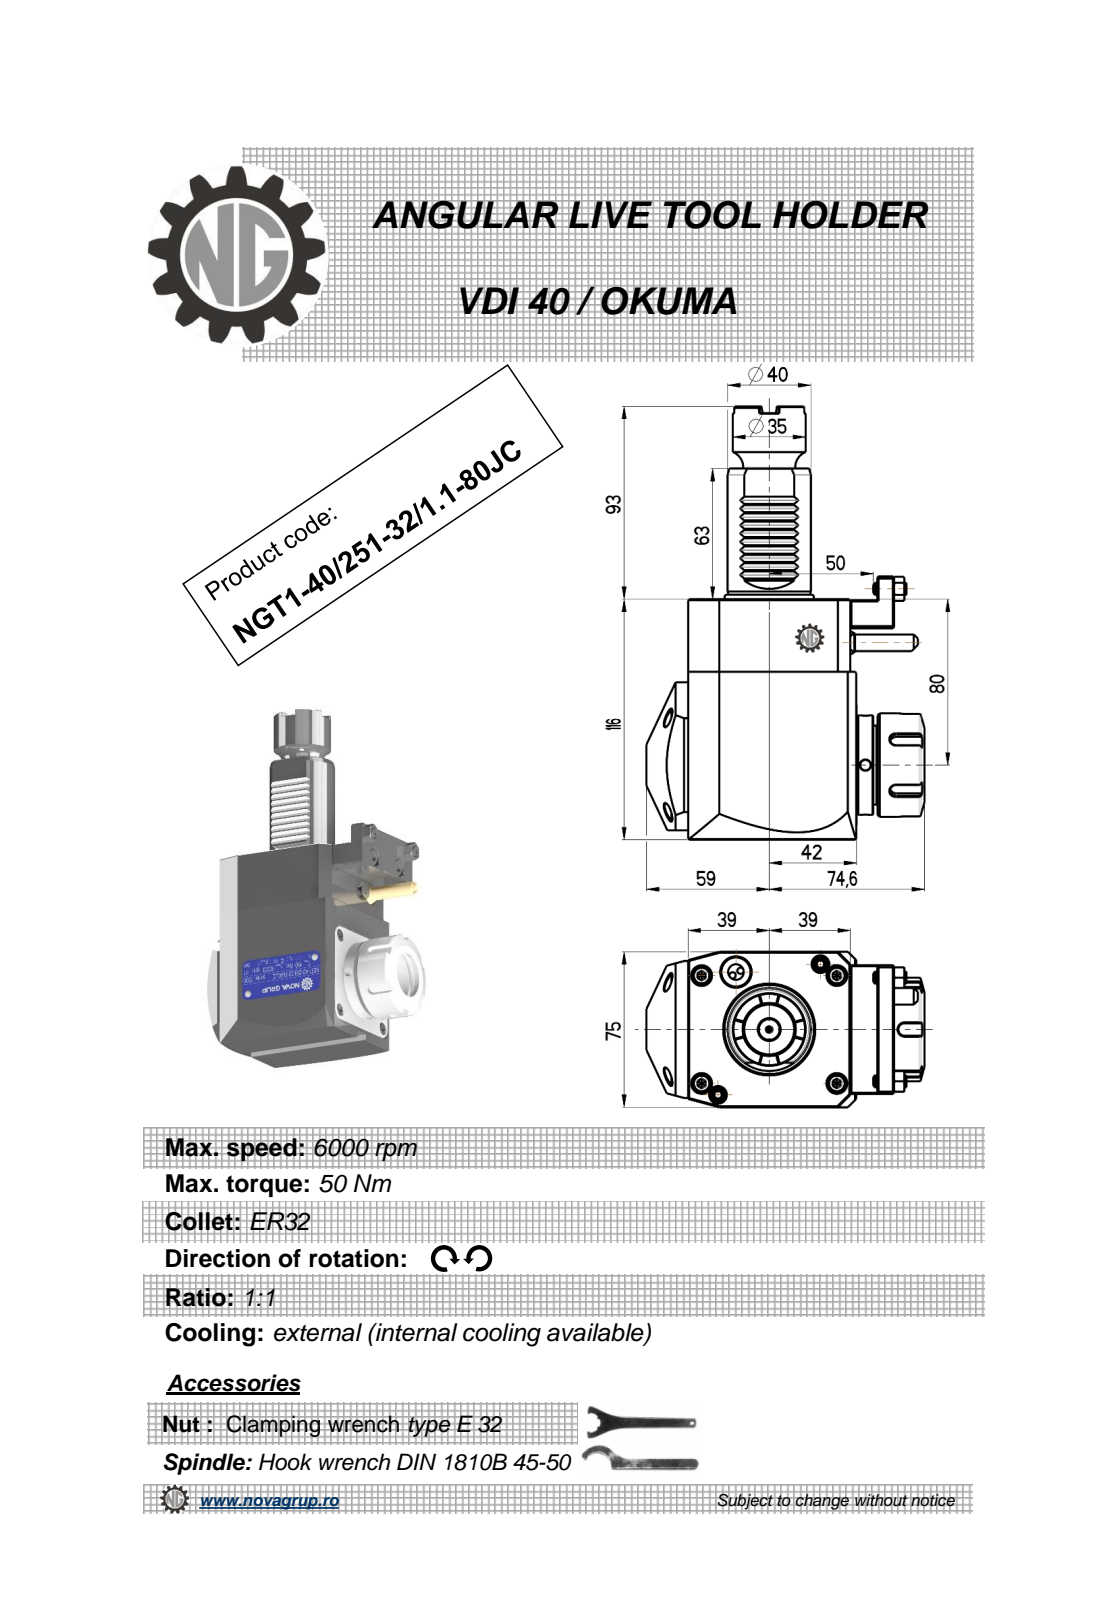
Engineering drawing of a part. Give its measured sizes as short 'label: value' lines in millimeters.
name: NGT1_40_251_32_1_1_80JC
written by: PRO/ENGINEER BY PARAMETRIC TECHNOLOGY CORPORATION, 2010280 (CONFIG_CONTROL_DESIGN)
unit: mm
bodies: 1 solid, 460 faces (195 planar, 86 cylindrical, 179 other)
size: 209 × 133.6 × 76.6
volume: 917 200 mm³; area: 75 631 mm²
holes: 3× ⌀5, 1× ⌀3, 1× ⌀25, 1× ⌀27
bosses: 2× ⌀6, 1× ⌀50, 1× ⌀48, 1× ⌀41, 1× ⌀40, 1× ⌀35, 1× ⌀10, 1× ⌀8
rounds: 10× R0.3, 10× R0.31, 6× R0.2, 5× R3, 1× R0.5, 1× R40
face distances: 75, 116, 81, 0.5, 18, 21, 80.8, 10, 3, 14
hole spacings: 46.25, 61.13
